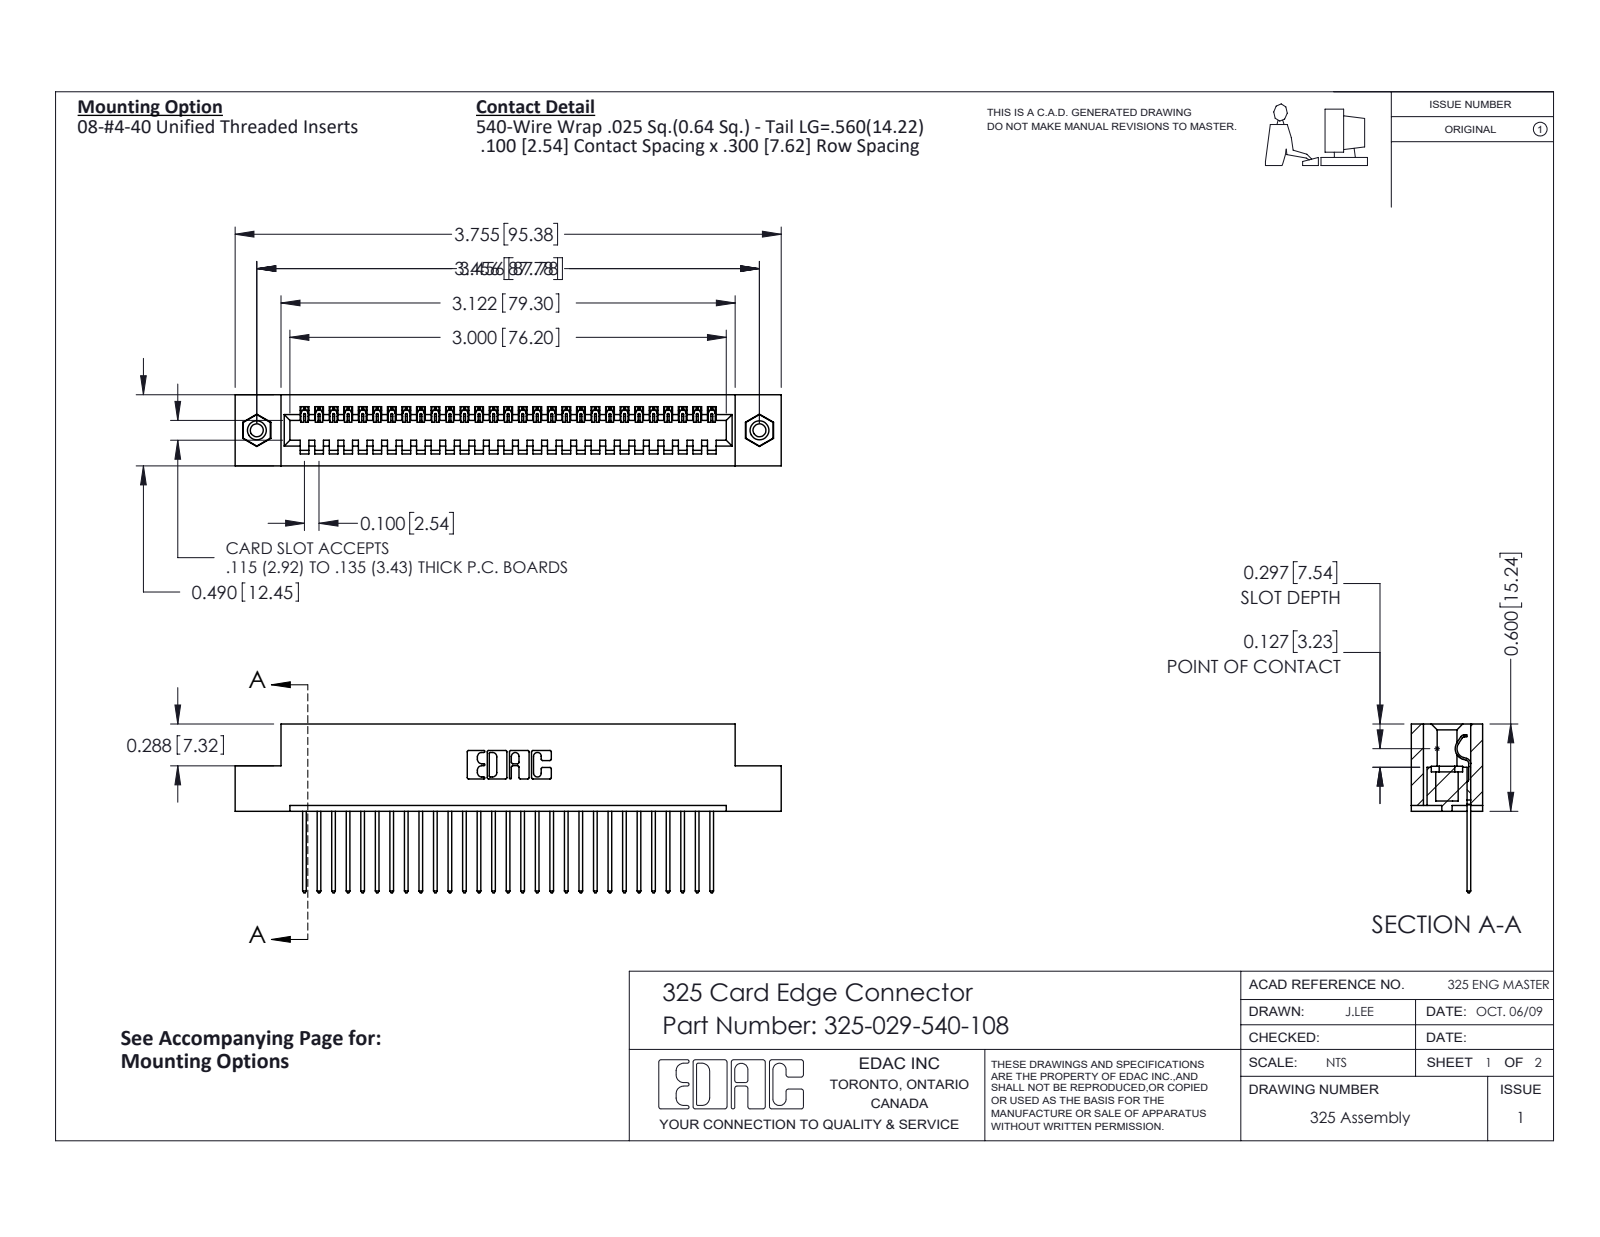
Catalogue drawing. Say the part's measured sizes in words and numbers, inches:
The part is named "325-292-001_325-293-140; 345-250-001_345-250-003-102; 325-029-540-108; 325 Part_TI". Its 3-D file was written by "SolidWorks 2016 (CONFIG_CONTROL_DESIGN)". It is 32 solids with 1856 faces: 1320 planar, 520 cylindrical and 16 other. Overall it measures 3.755 by 1.16 by 0.49 inches. Its volume is 0.735 cubic inches and its surface area 20.52 square inches. Round holes: 2 of diameter 0.089, 2 of diameter 0.125, 2 of diameter 0.16. Round bosses or shafts: 2 of diameter 0.155. Partial cylindrical surfaces (rounded edges, fillets, slot ends): 58 of radius 0.006, 58 of radius 0.01, 22 of radius 0.01, 6 of radius 0.007, 6 of radius 0.031, 3 of radius 0.026, 1 of radius 0.014, 1 of radius 0.022. The main face-to-face distances are 0.083, 0.407, 0.49, 0.3, 0.107, 0.383, 0.025, 0.325, 0.04, 0.56. The hole center spacings are 3.456.
